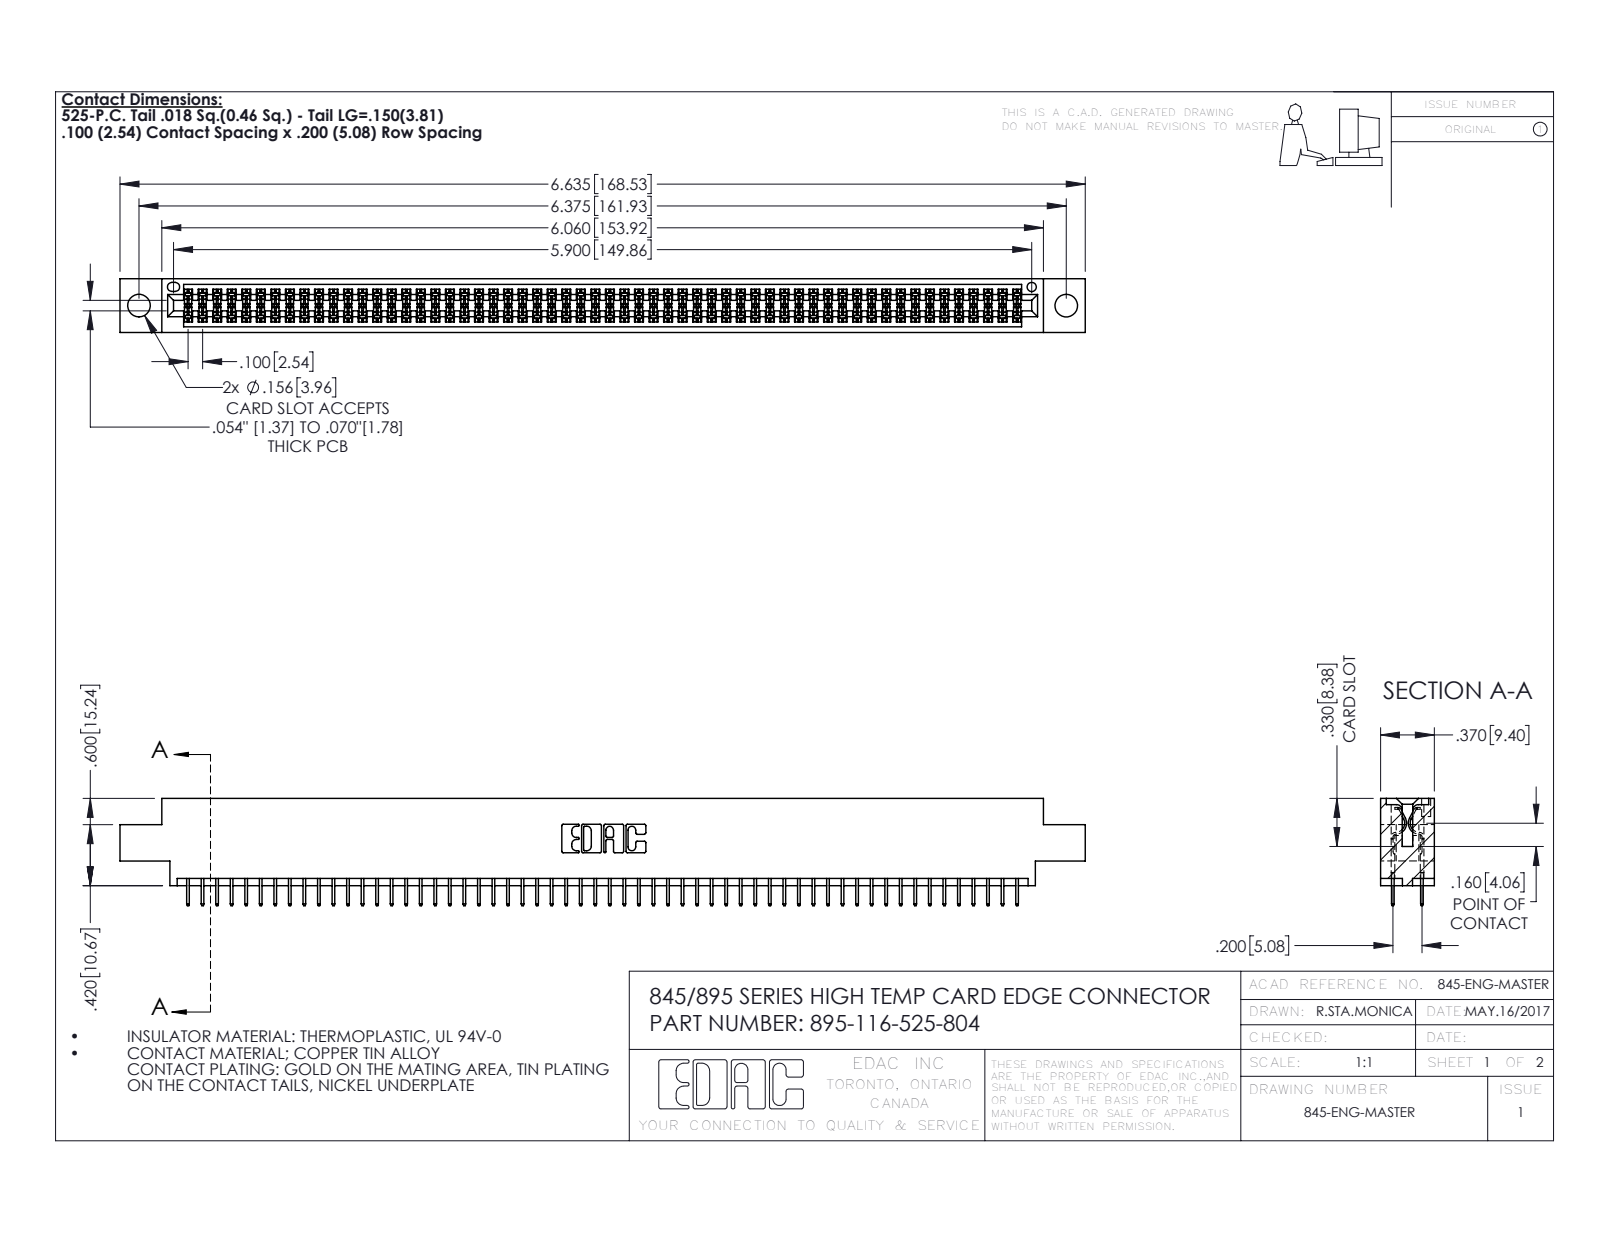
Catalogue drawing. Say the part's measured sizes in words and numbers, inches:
The part is named "345-292-001_345-293-125; 345 Part_0.170 Offset - 0.156 Dia-TH; 395-116-525-804". Its 3-D file was written by "SolidWorks 2020 (CONFIG_CONTROL_DESIGN)". It is 117 solids with 6394 faces: 4608 planar, 1786 cylindrical and 0 other. Overall it measures 6.635 by 0.737 by 0.37 inches. Its volume is 0.984 cubic inches and its surface area 36.47 square inches. Round holes: 2 of diameter 0.156, 1 of diameter 0.064. Partial cylindrical surfaces (rounded edges, fillets, slot ends): 174 of radius 0.006, 22 of radius 0.01, 6 of radius 0.007, 6 of radius 0.031, 3 of radius 0.026, 2 of radius 0.014, 2 of radius 0.019, 2 of radius 0.022. The main face-to-face distances are 0.072, 0.298, 0.37, 0.2, 0.098, 0.272, 0.025, 0.225, 0.175, 0.072. The hole center spacings are 0.27, 6.139, 6.375.
